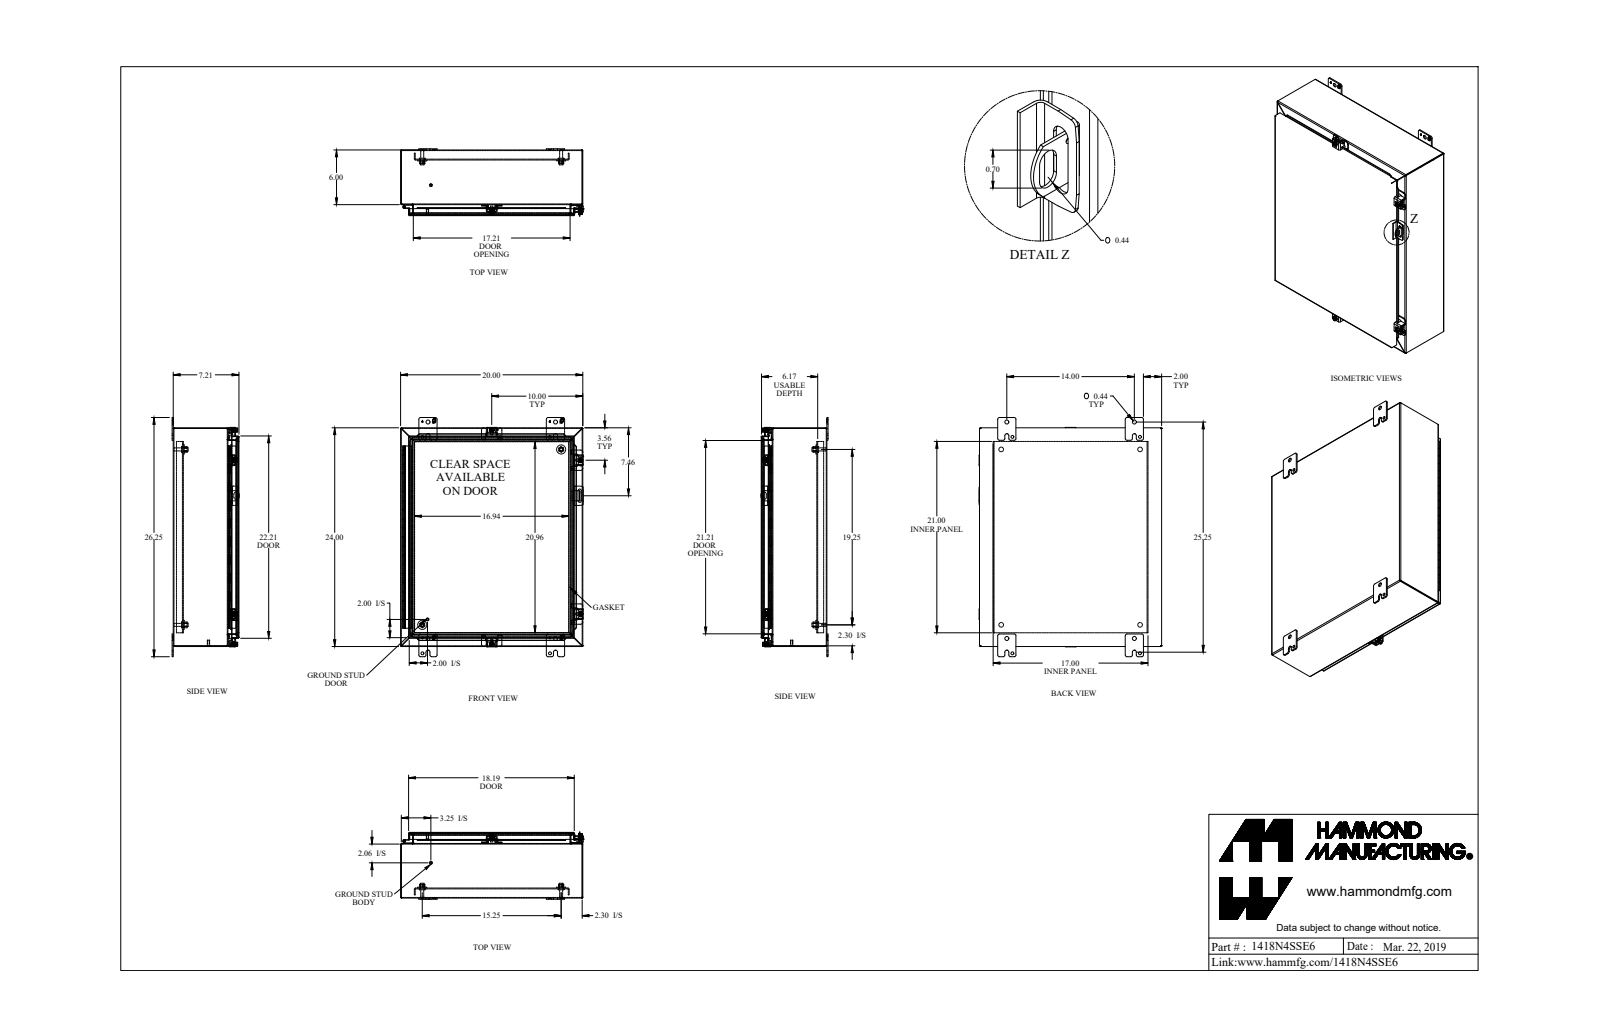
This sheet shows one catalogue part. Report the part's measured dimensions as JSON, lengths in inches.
{"part_name": "1418N4SSE6_Default", "step_written_by": "SolidWorks 2019 (CONFIG_CONTROL_DESIGN)", "units": "inches", "bodies": {"solids": 39, "faces": 1499, "planar": 925, "cylindrical": 481, "other": 93}, "overall_size": [26.25, 20.063, 7.375], "volume_in3": 172.2, "surface_area_in2": 4519, "round_holes": [[0.213, 4], [0.313, 4], [0.375, 4], [0.437, 4], [0.5, 4], [0.265, 2], [0.265, 2], [0.307, 2], [0.445, 2], [0.125, 1], [0.187, 1]], "round_bosses_or_shafts": [[0.65, 4], [0.5, 4], [0.39, 4], [0.375, 4], [0.332, 4], [0.244, 4], [1, 2], [0.313, 2]], "partial_cylinders_radius": [[0.188, 26], [0.036, 24], [0.108, 24], [0.048, 21], [0.143, 21], [0.25, 20], [0.125, 10], [0.045, 8]], "face_to_face_distances": [0.072, 7.066, 7.138, 0.072, 7.138, 7.21, 0.095, 0.937, 1.009, 6.106], "hole_center_spacings": [7.916, 22.694, 14, 24.559, 1.735, 2.434, 14.702, 15.25]}
